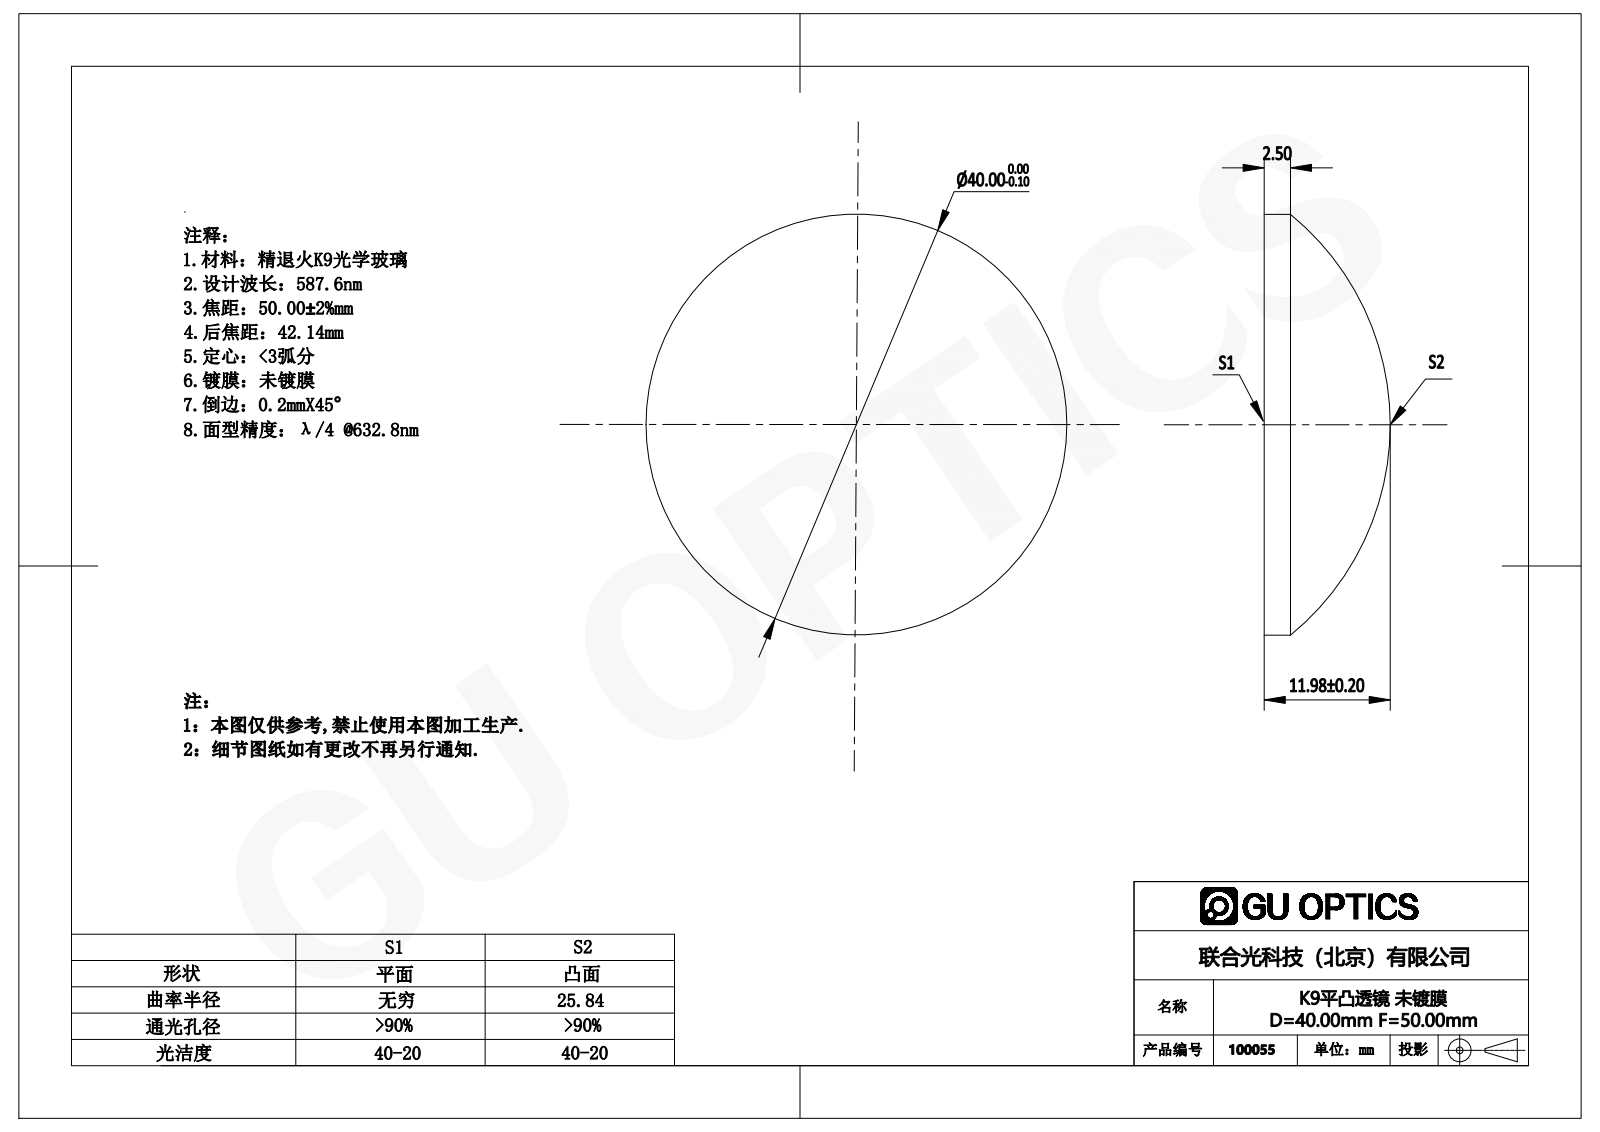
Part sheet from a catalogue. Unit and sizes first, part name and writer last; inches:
Units: inches
Overall size (bounding box): 1.575 × 1.575 × 0.472
Round bosses / shafts (diameter × count): ⌀1.575 ×1
Volume: 0.582 in³ · Surface area: 4.821 in²
Bodies: 1 solid, 5 faces (1 planar, 2 cylindrical, 2 other)
Part name (STEP PRODUCT): 100055
STEP written by: SolidWorks 2016 (AUTOMOTIVE_DESIGN)
